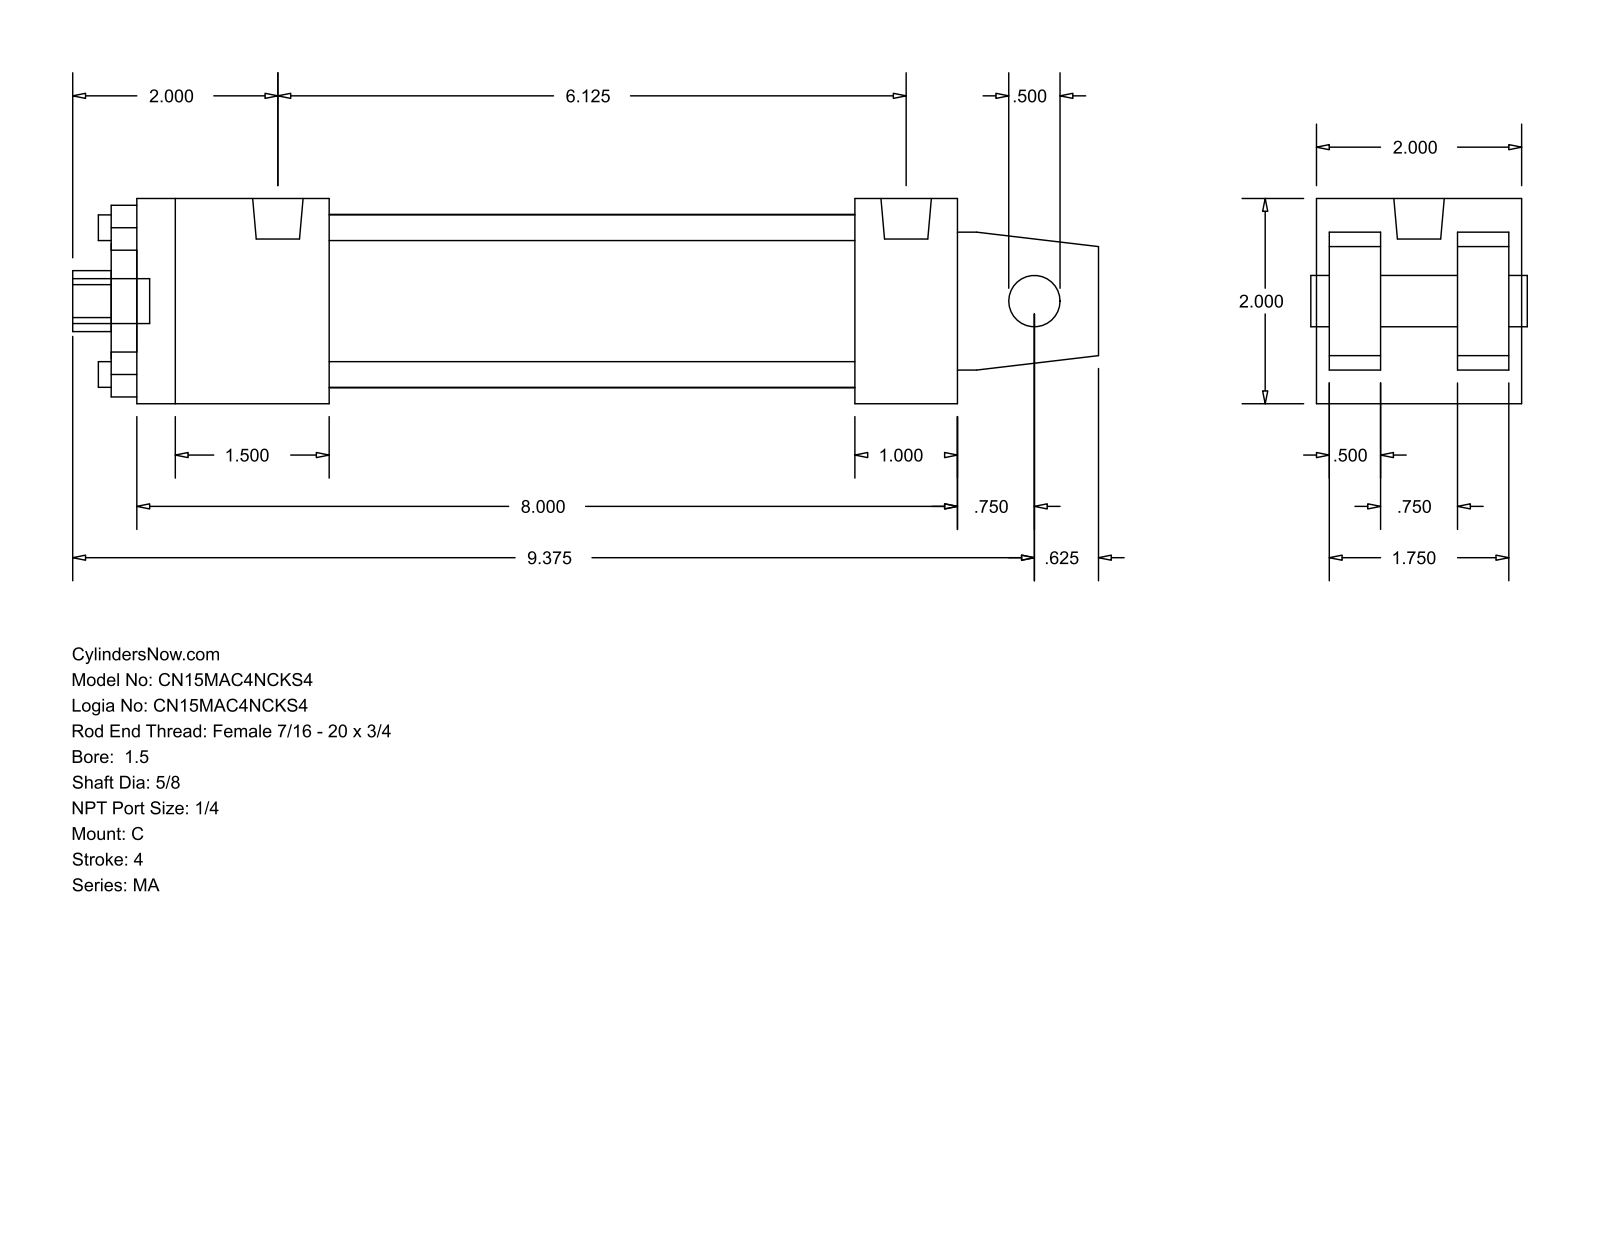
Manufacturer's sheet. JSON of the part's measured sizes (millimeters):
{"part_name": "MA_C__0150_0.625", "step_written_by": "GSSL Pune (CONFIG_CONTROL_DESIGN)", "units": "millimeters", "bodies": {"solids": 0, "faces": 103, "planar": 76, "cylindrical": 27, "other": 0}, "overall_size": [254, 50.8, 50.8], "round_holes": [[6.35, 4], [12.7, 1], [15.88, 1], [28.57, 1], [42.93, 1]], "round_bosses_or_shafts": [[7.94, 4], [12.49, 2], [11.11, 1]], "partial_cylinders_radius": [[7.54, 1]], "face_to_face_distances": [50.8, 34.93, 12.7, 3.17, 15.87, 47.63, 31.76, 203.19, 177.8, 25.39], "hole_center_spacings": [25.68, 36.32, 51.36]}
